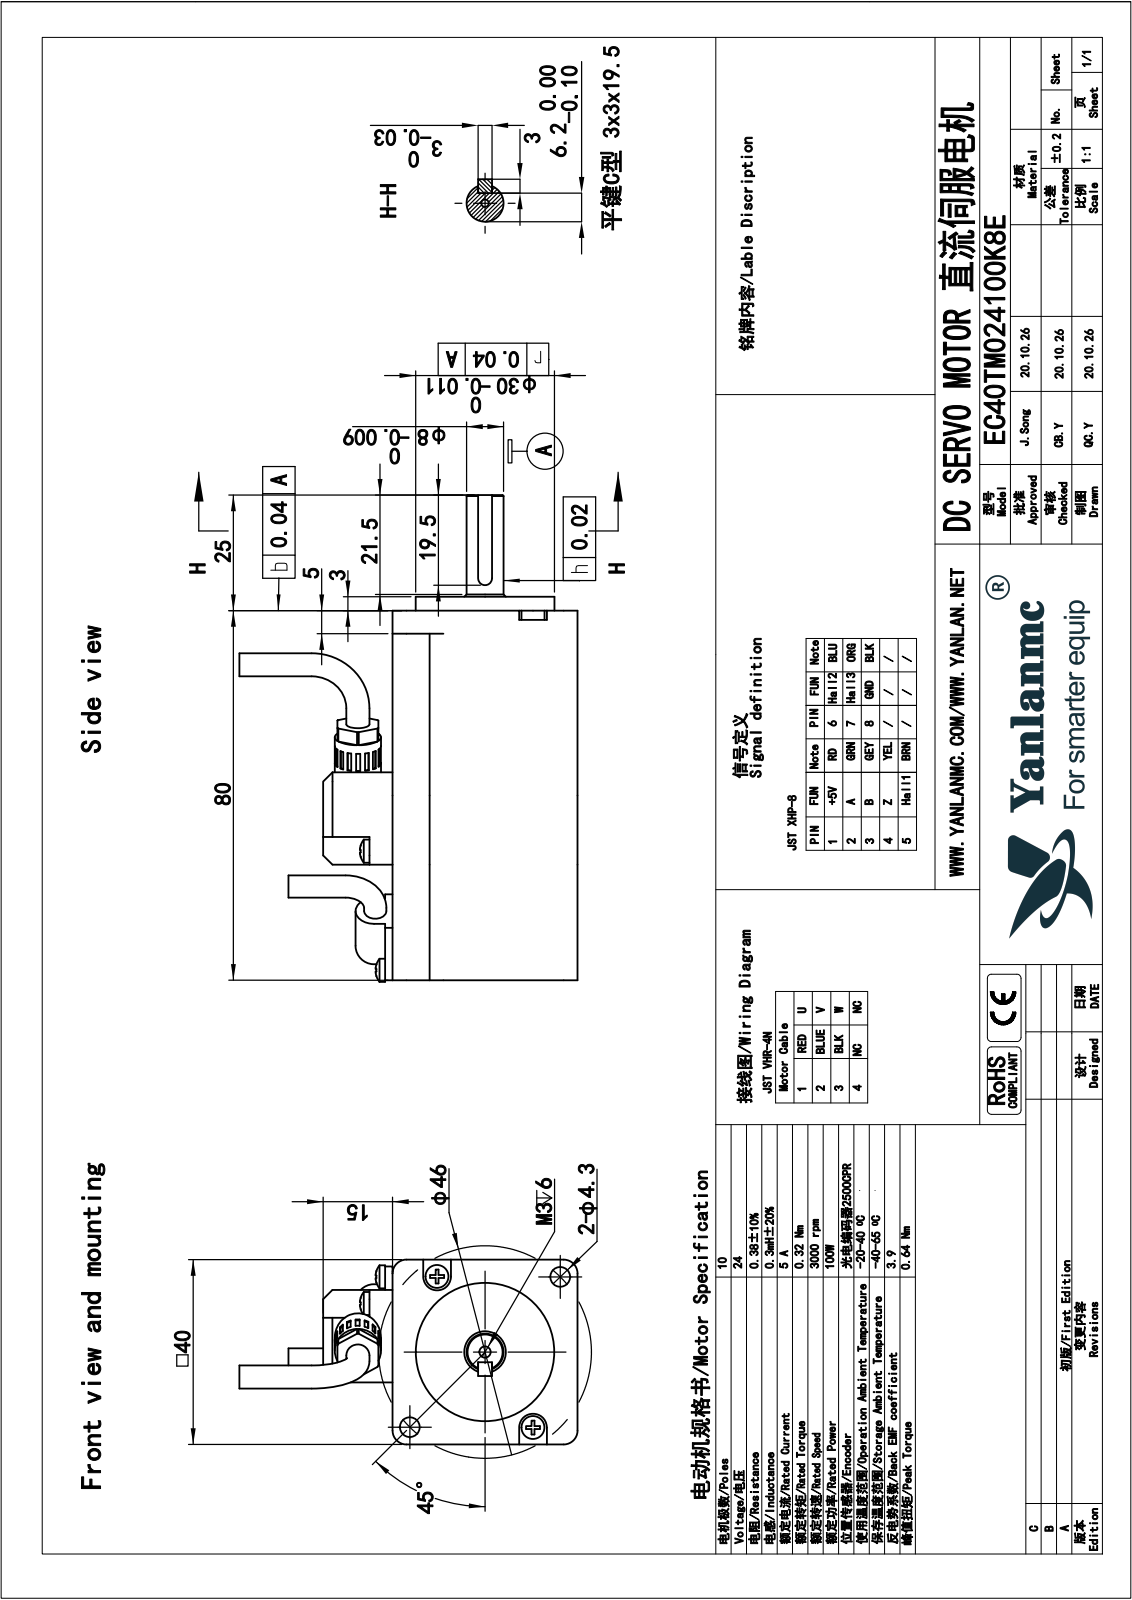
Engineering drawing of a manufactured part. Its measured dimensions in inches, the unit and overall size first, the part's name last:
Units: inches
Overall size (bounding box): 4.148 × 2.879 × 1.575
Round holes (diameter × count): ⌀0.096 ×2, ⌀0.118 ×2, ⌀0.169 ×2, ⌀0.098 ×1
Round bosses / shafts (diameter × count): ⌀0.197 ×8, ⌀0.098 ×4, ⌀0.189 ×2, ⌀1.181 ×1, ⌀0.394 ×1, ⌀0.315 ×1
Partial cylindrical surfaces — rounded edges, fillets, slot ends (radius × count): R0.012 ×16, R0.118 ×10, R0.079 ×4, R0.157 ×2, R0.197 ×2, R0.059 ×1
Main face-to-face distances: 1.575, 3.15, 0.118, 3.268, 2.165, 0.787, 0.236, 0.315, 0.551, 0.591
Hole centre spacings: 0.653, 0.787, 0.906, 0.906, 0.966, 1.062, 1.143, 1.591
Volume: 7.913 in³ · Surface area: 32.7 in²
Bodies: 8 solids, 368 faces (242 planar, 104 cylindrical, 22 other)
Part name (STEP PRODUCT): ПЯ1; ПЯ2; M2.5X10_ M2.5X10
STEP written by: SolidWorks 2020 (AUTOMOTIVE_DESIGN)
